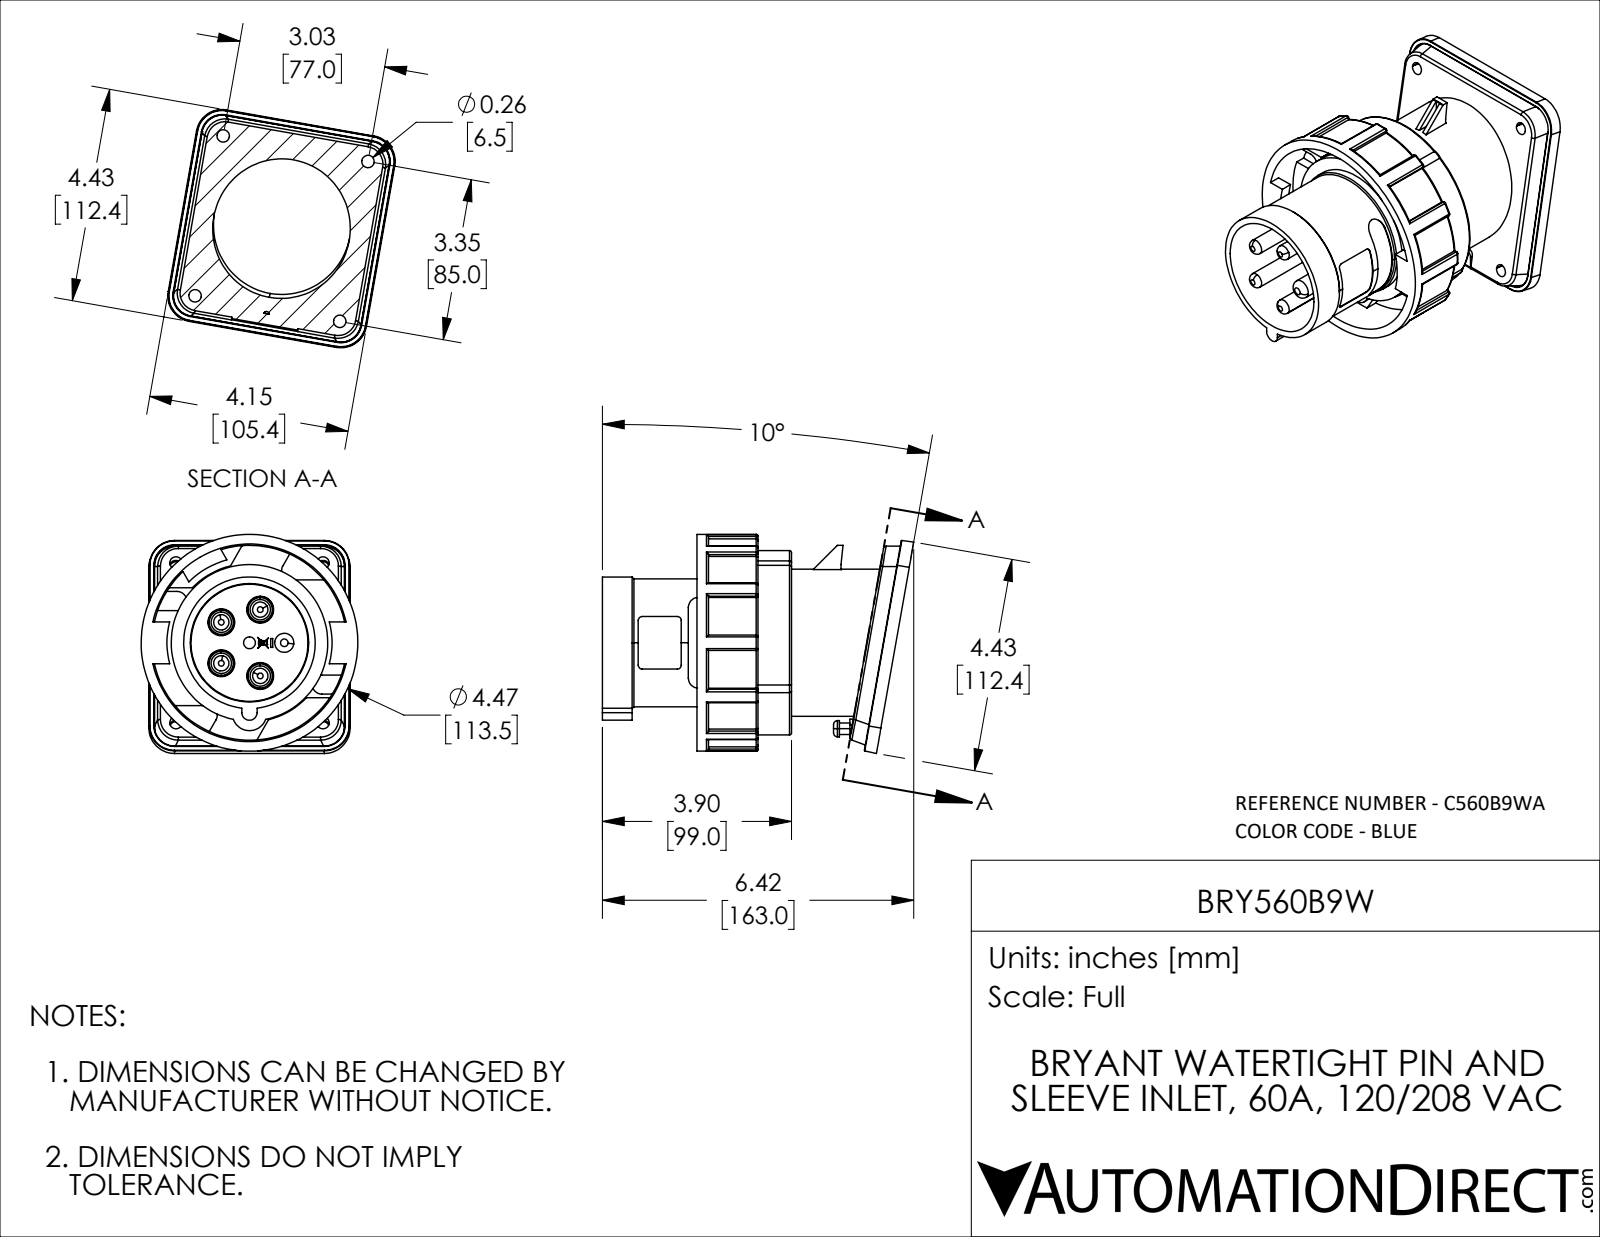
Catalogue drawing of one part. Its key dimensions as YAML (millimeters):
part_name: "BRY560B9W"
step_written_by: "SolidWorks 2021 (CONFIG_CONTROL_DESIGN)"
units: millimeters
bodies: {solids: 1, faces: 1547, planar: 704, cylindrical: 553, other: 290}
overall_size: [163.03, 114.7, 113.5]
volume: 450323
surface_area: 155806
round_holes:
  - {diameter: 3, count: 2}
  - {diameter: 0.51, count: 1}
  - {diameter: 3.2, count: 1}
  - {diameter: 3.6, count: 1}
  - {diameter: 6.2, count: 1}
  - {diameter: 62, count: 1}
  - {diameter: 72, count: 1}
  - {diameter: 81, count: 1}
  - {diameter: 103.5, count: 1}
round_bosses_or_shafts:
  - {diameter: 5, count: 6}
  - {diameter: 8, count: 4}
  - {diameter: 113.5, count: 1}
  - {diameter: 102, count: 1}
  - {diameter: 96.5, count: 1}
  - {diameter: 82, count: 1}
  - {diameter: 77, count: 1}
  - {diameter: 68.9, count: 1}
partial_cylinders:
  - {radius: 0.5, count: 91}
  - {radius: 1, count: 45}
  - {radius: 5, count: 13}
  - {radius: 0.25, count: 8}
  - {radius: 3.25, count: 8}
  - {radius: 0.15, count: 7}
  - {radius: 2, count: 6}
  - {radius: 1.5, count: 5}
face_to_face_distances: [15.02, 49.5, 12.5, 15, 5, 32.5, 17.5, 37, 11, 17]
hole_center_spacings: [0.8, 8.18, 8.98, 14.17, 21.3, 21.31, 22.26, 23.03]
